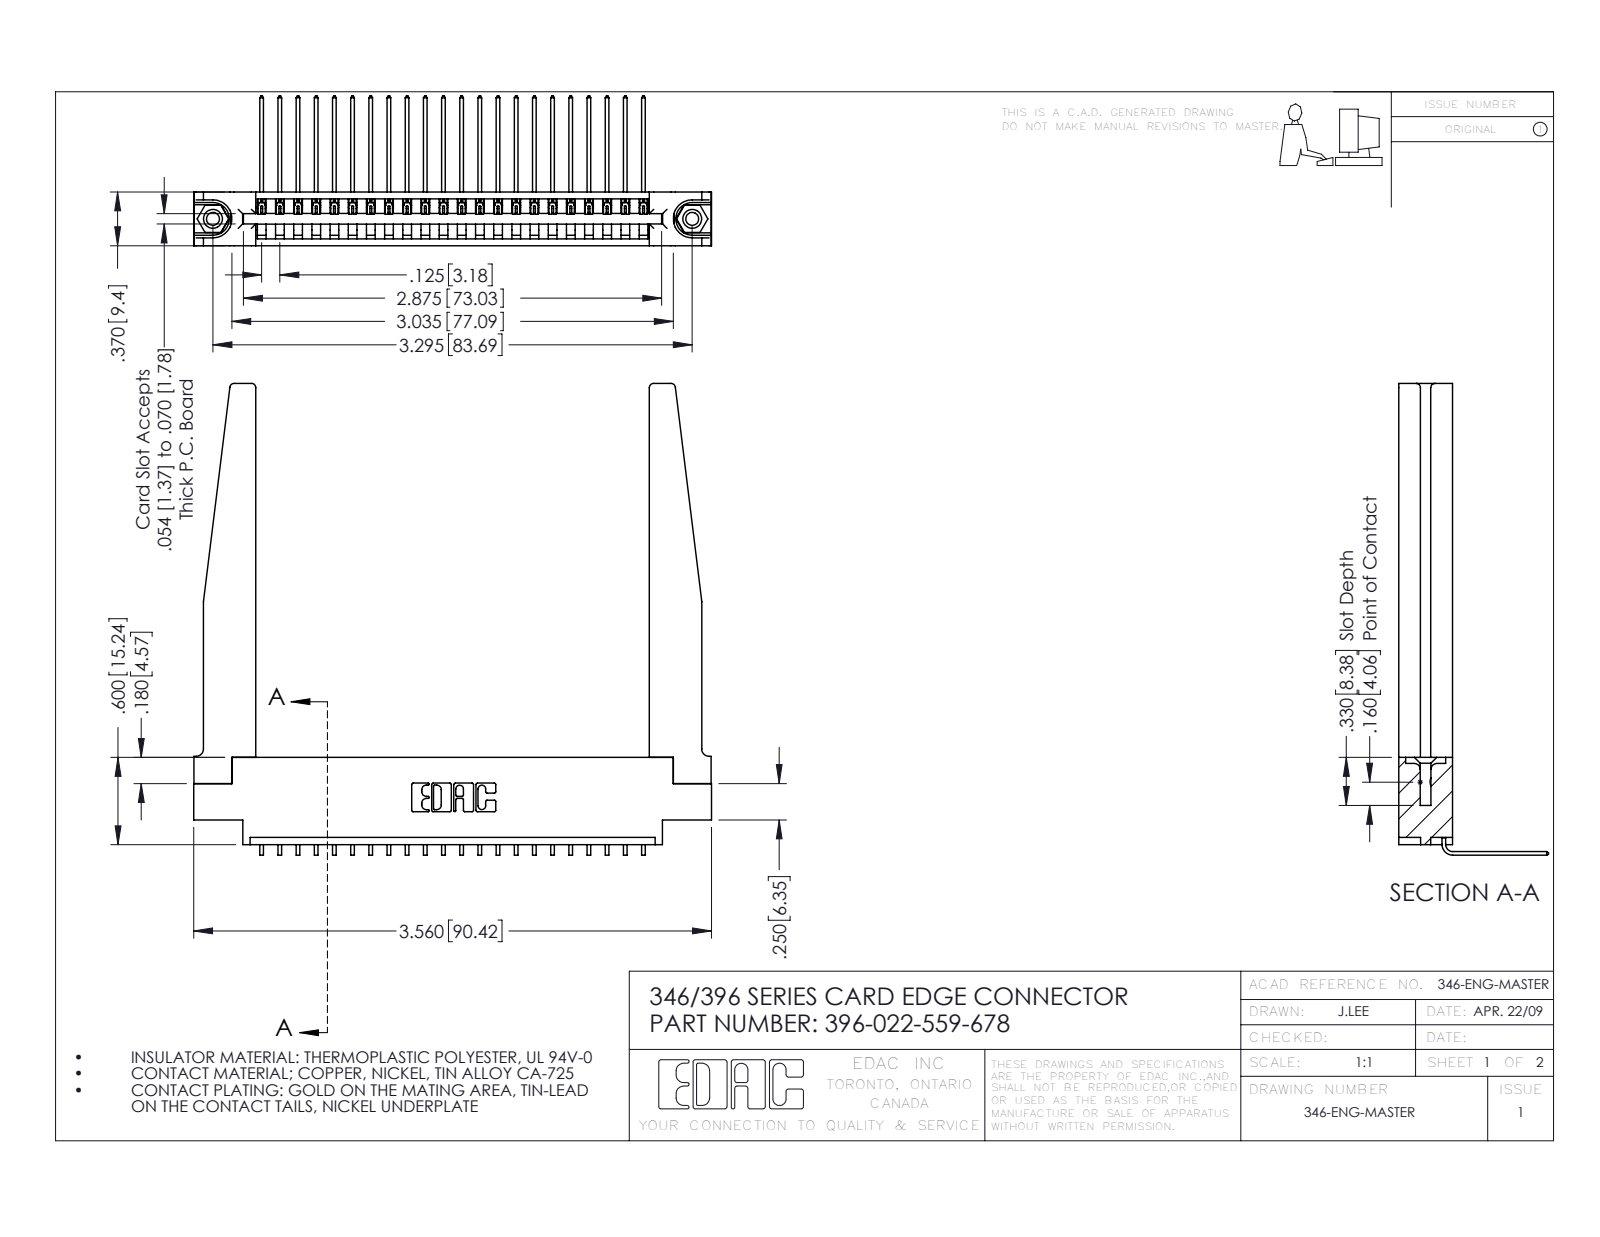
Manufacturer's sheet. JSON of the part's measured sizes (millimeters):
{"part_name": "345-250-001_345-250-001-102; 346-220-078_345-220-078; 396-022-559-678; 345-292-001_558 559 Tail - 1 (+1 more)", "step_written_by": "SolidWorks 2016 (CONFIG_CONTROL_DESIGN)", "units": "millimeters", "bodies": {"solids": 27, "faces": 1680, "planar": 1146, "cylindrical": 482, "other": 52}, "overall_size": [90.4, 82.4, 26.2], "volume_mm3": 15300, "surface_area_mm2": 17460, "round_holes": [[2.3, 2], [3.2, 2], [4, 2], [1.6, 1]], "round_bosses_or_shafts": [[3.9, 2]], "partial_cylinders_radius": [[0.2, 44], [0.3, 22], [0.8, 8], [0.2, 6], [0.8, 6], [0.7, 3], [1.3, 3], [0.8, 2]], "face_to_face_distances": [9.4, 1.8, 1.2, 8.2, 3.8, 3.8, 0.6, 6.4, 7.6, 5.6], "hole_center_spacings": [6.2, 78.4, 83.7]}
